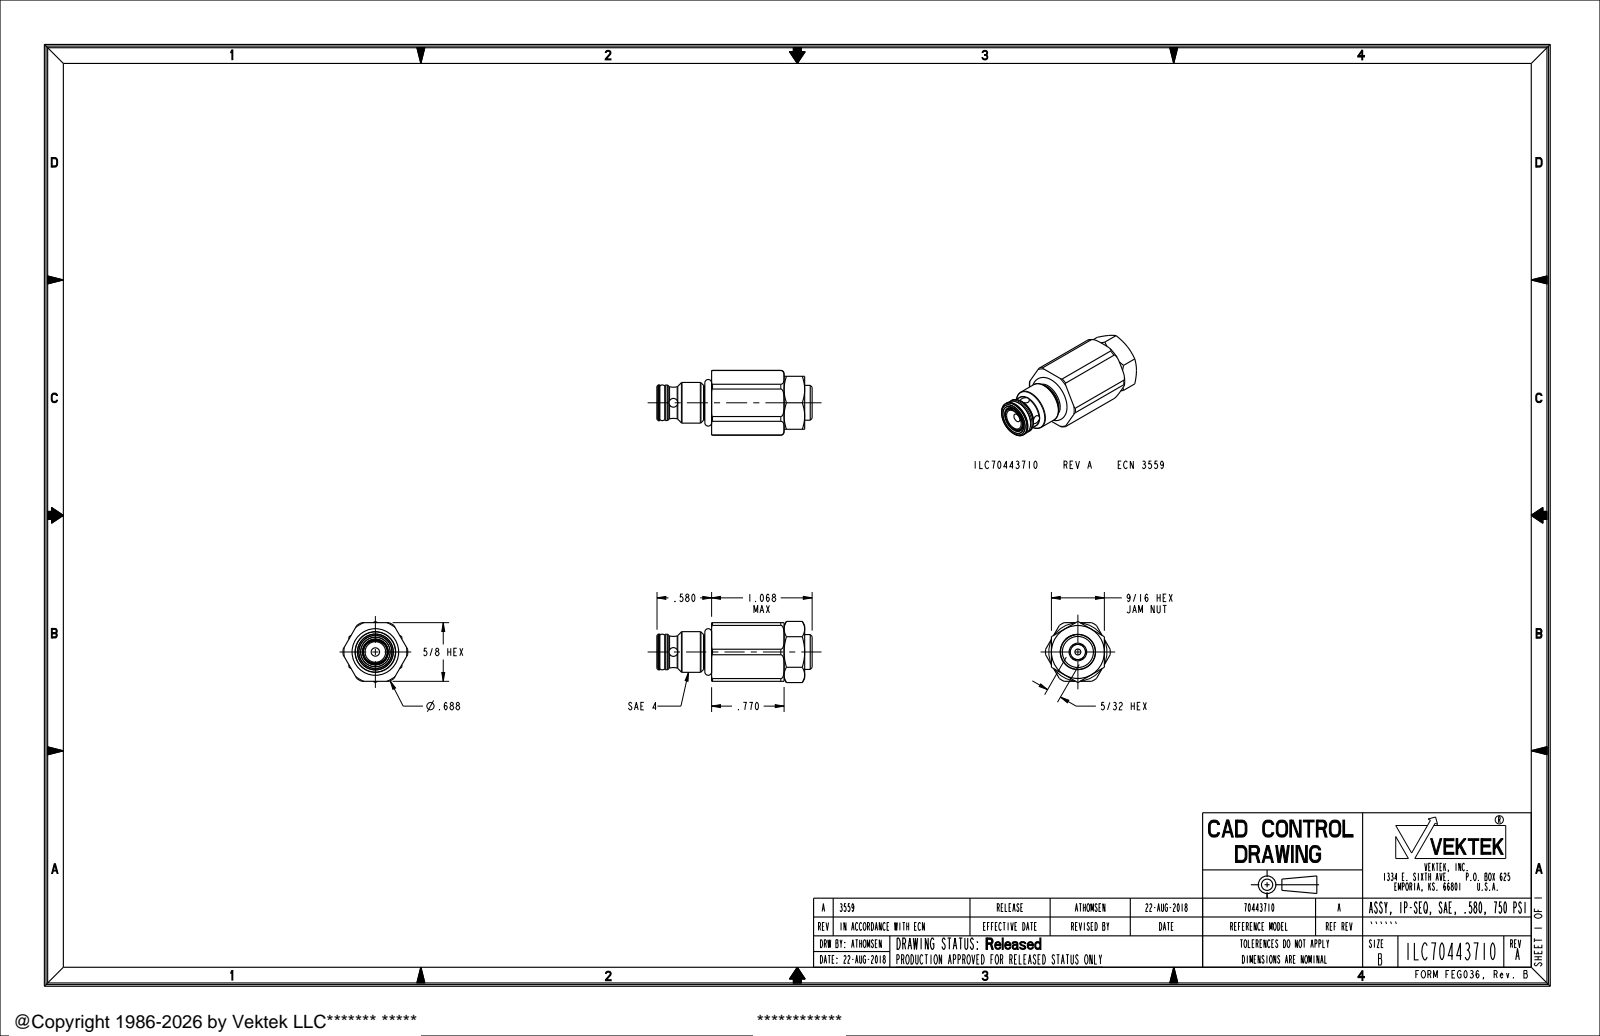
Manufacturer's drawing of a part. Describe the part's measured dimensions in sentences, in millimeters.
The part is named "ILC70443710". Its 3-D file was written by "PRO/ENGINEER BY PARAMETRIC TECHNOLOGY CORPORATION, 2013320 (AUTOMOTIVE_DESIGN)". It is 1 solid with 214 faces: 45 planar, 69 cylindrical and 100 other. Overall it measures 41.9 by 17.5 by 16.5 millimeters. Its volume is 6 330 cubic millimeters and its surface area 2 927 square millimeters. Round holes: 2 of diameter 2.4, 1 of diameter 4.1, 1 of diameter 6.3, 1 of diameter 6.9, 1 of diameter 9.5, 1 of diameter 12.7, 1 of diameter 13.4. Round bosses or shafts: 1 of diameter 11, 1 of diameter 9.7, 1 of diameter 9.6, 1 of diameter 9.4, 1 of diameter 9.2, 1 of diameter 8.7, 1 of diameter 6. Partial cylindrical surfaces (rounded edges, fillets, slot ends): 2 of radius 2.9, 1 of radius 2.4, 1 of radius 8.7. The main face-to-face distances are 15.8, 14.3, 19.6, 5.6, 25.1, 1.3, 6.9, 18.2, 2, 7.6.
